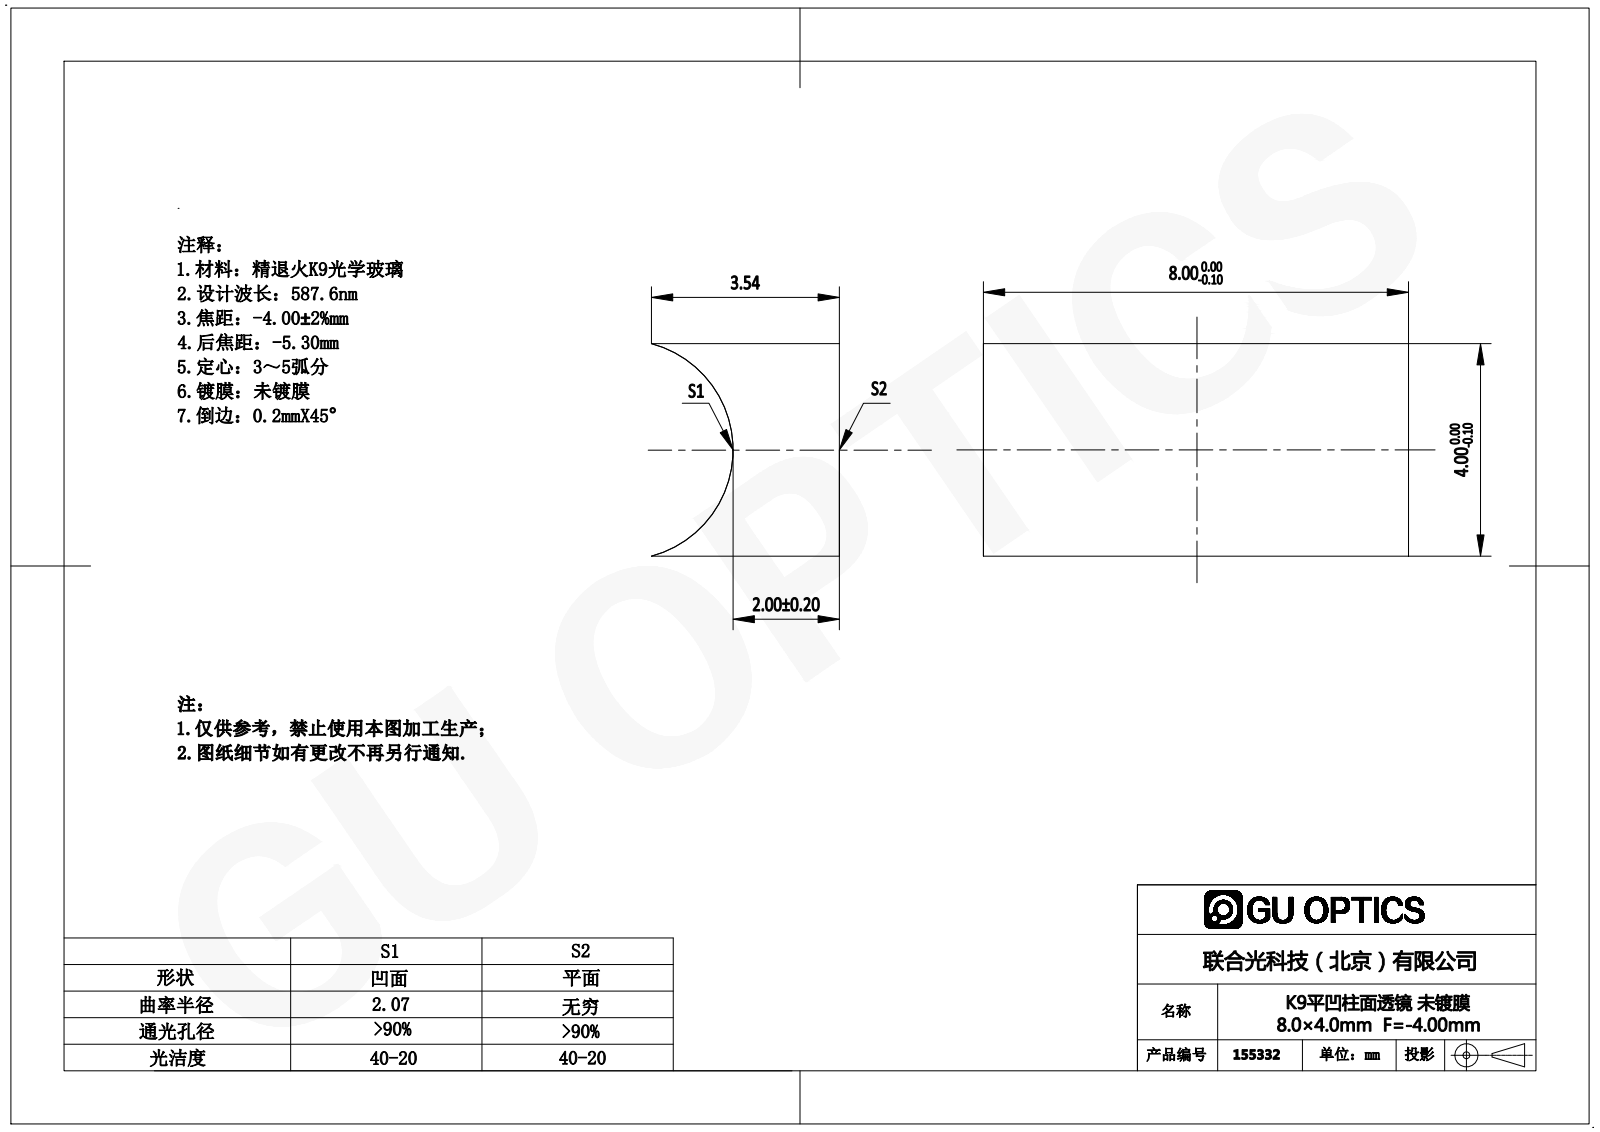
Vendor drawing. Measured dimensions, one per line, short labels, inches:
name: 155332
written by: SolidWorks 2016 (AUTOMOTIVE_DESIGN)
unit: in
bodies: 1 solid, 6 faces (5 planar, 1 cylindrical, 0 other)
size: 0.315 × 0.157 × 0.139
volume: 0.005 in³; area: 0.234 in²
rounds: 1× R0.081
face distances: 0.157, 0.315
